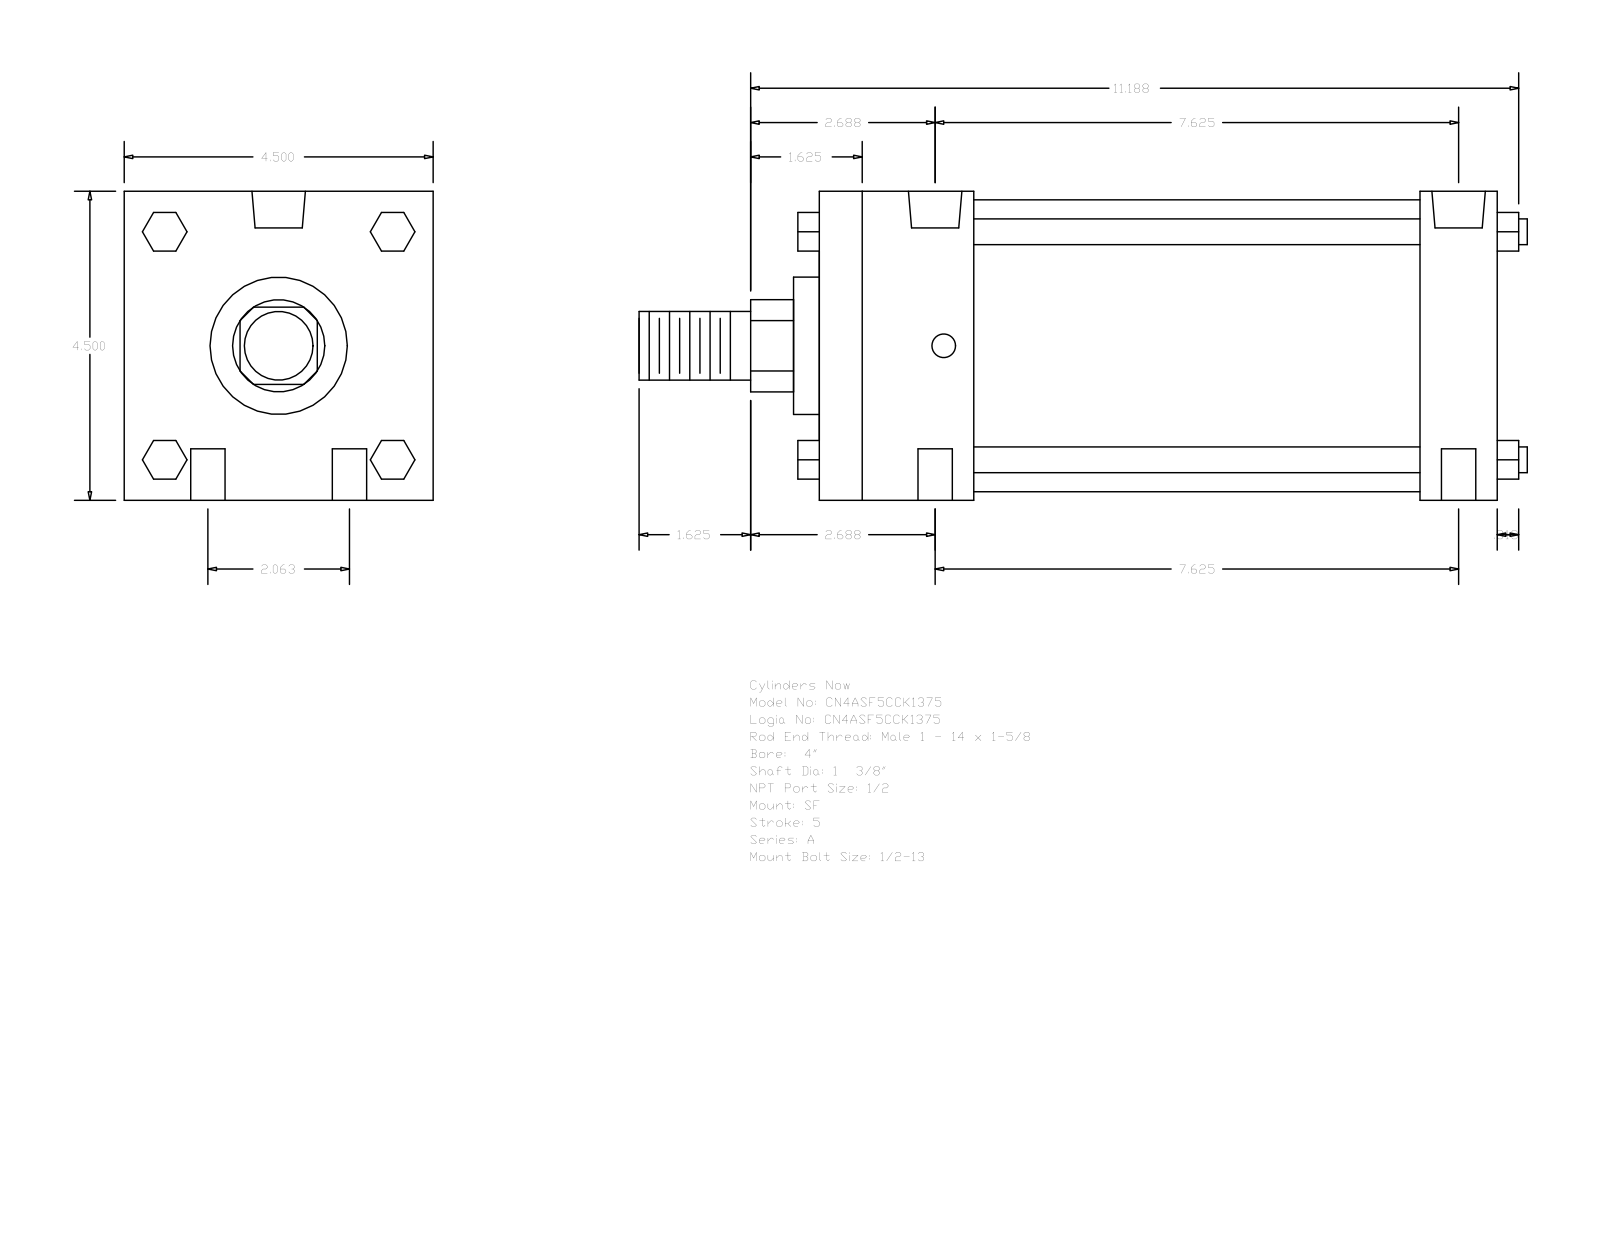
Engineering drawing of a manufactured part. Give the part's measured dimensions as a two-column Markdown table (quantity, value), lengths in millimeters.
| quantity | value |
| --- | --- |
| part name | A_SF__0400_1.375 |
| STEP written by | GSSL Pune (CONFIG_CONTROL_DESIGN) |
| units | millimeters |
| bodies | 0 solids, 124 faces (94 planar, 30 cylindrical, 0 other) |
| overall size | 328.61 × 114.3 × 114.3 |
| round holes (diameter × count) | 12.7 × 4, 8.73 × 2, 19.77 × 2 |
| round bosses / shafts (diameter × count) | 9.53 × 4, 107.95 × 1, 50.8 × 1, 34.92 × 1, 25.4 × 1 |
| partial cylindrical surfaces (radius × count) | 17.06 × 1 |
| main face-to-face distances | 114.3, 250.83, 57.15, 28.58, 222.25, 165.1, 193.68, 66.67, 14.29, 9.52 |
| hole center spacings | 26.19, 195.44, 193.68, 52.38, 200.64, 187.32 |
